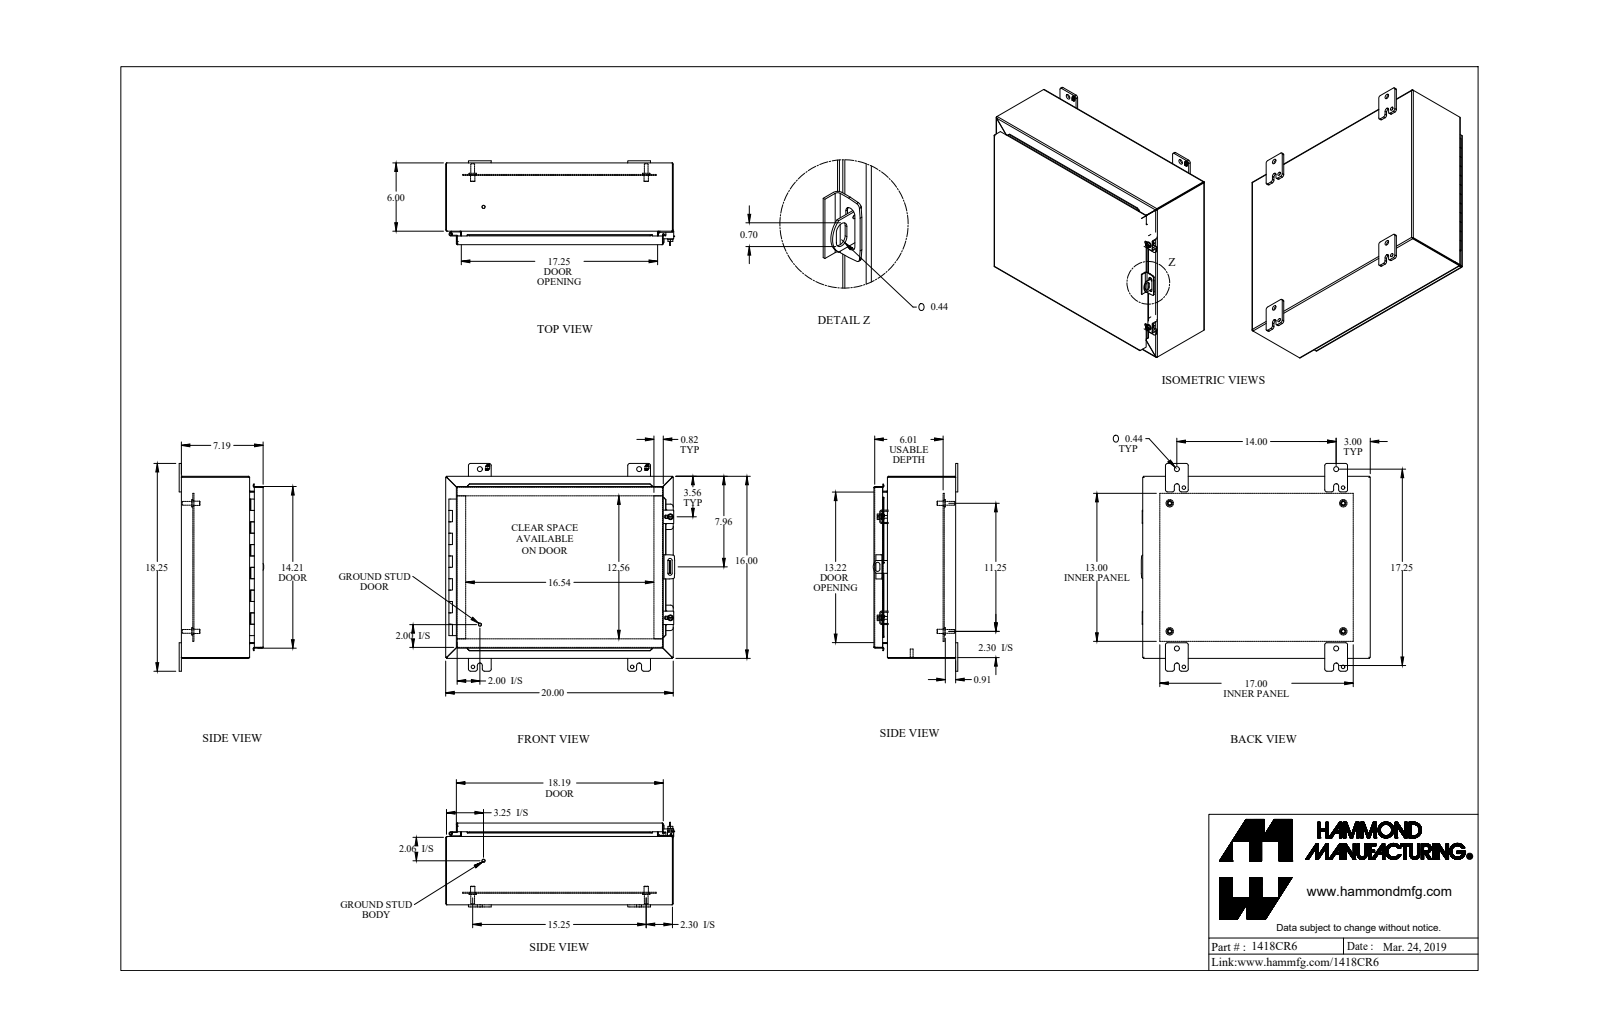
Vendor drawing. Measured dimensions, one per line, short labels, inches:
name: 1418CR6
written by: SolidWorks 2019 (AUTOMOTIVE_DESIGN)
unit: in
bodies: 38 solids, 954 faces (657 planar, 243 cylindrical, 54 other)
size: 20.125 × 18.25 × 7.437
volume: 125 in³; area: 3 230 in²
holes: 4× ⌀0.313, 4× ⌀0.437, 4× ⌀0.5, 2× ⌀0.213, 2× ⌀0.265, 2× ⌀0.307, 2× ⌀0.375, 2× ⌀0.445, 1× ⌀0.125, 1× ⌀0.187
bosses: 4× ⌀0.65, 4× ⌀0.375, 4× ⌀0.33, 2× ⌀1, 2× ⌀0.5, 2× ⌀0.39, 2× ⌀0.281, 2× ⌀0.25
rounds: 26× R0.188, 20× R0.036, 20× R0.108, 13× R0.048, 13× R0.143, 8× R0.007, 8× R0.045, 8× R0.079
face distances: 0.072, 7.113, 7.041, 7.185, 0.937, 1.009, 15.928, 0.095, 6.081, 6.009
hole spacings: 14, 15.25, 18.951, 21.073, 17.416, 19.402, 1.735, 1.736
